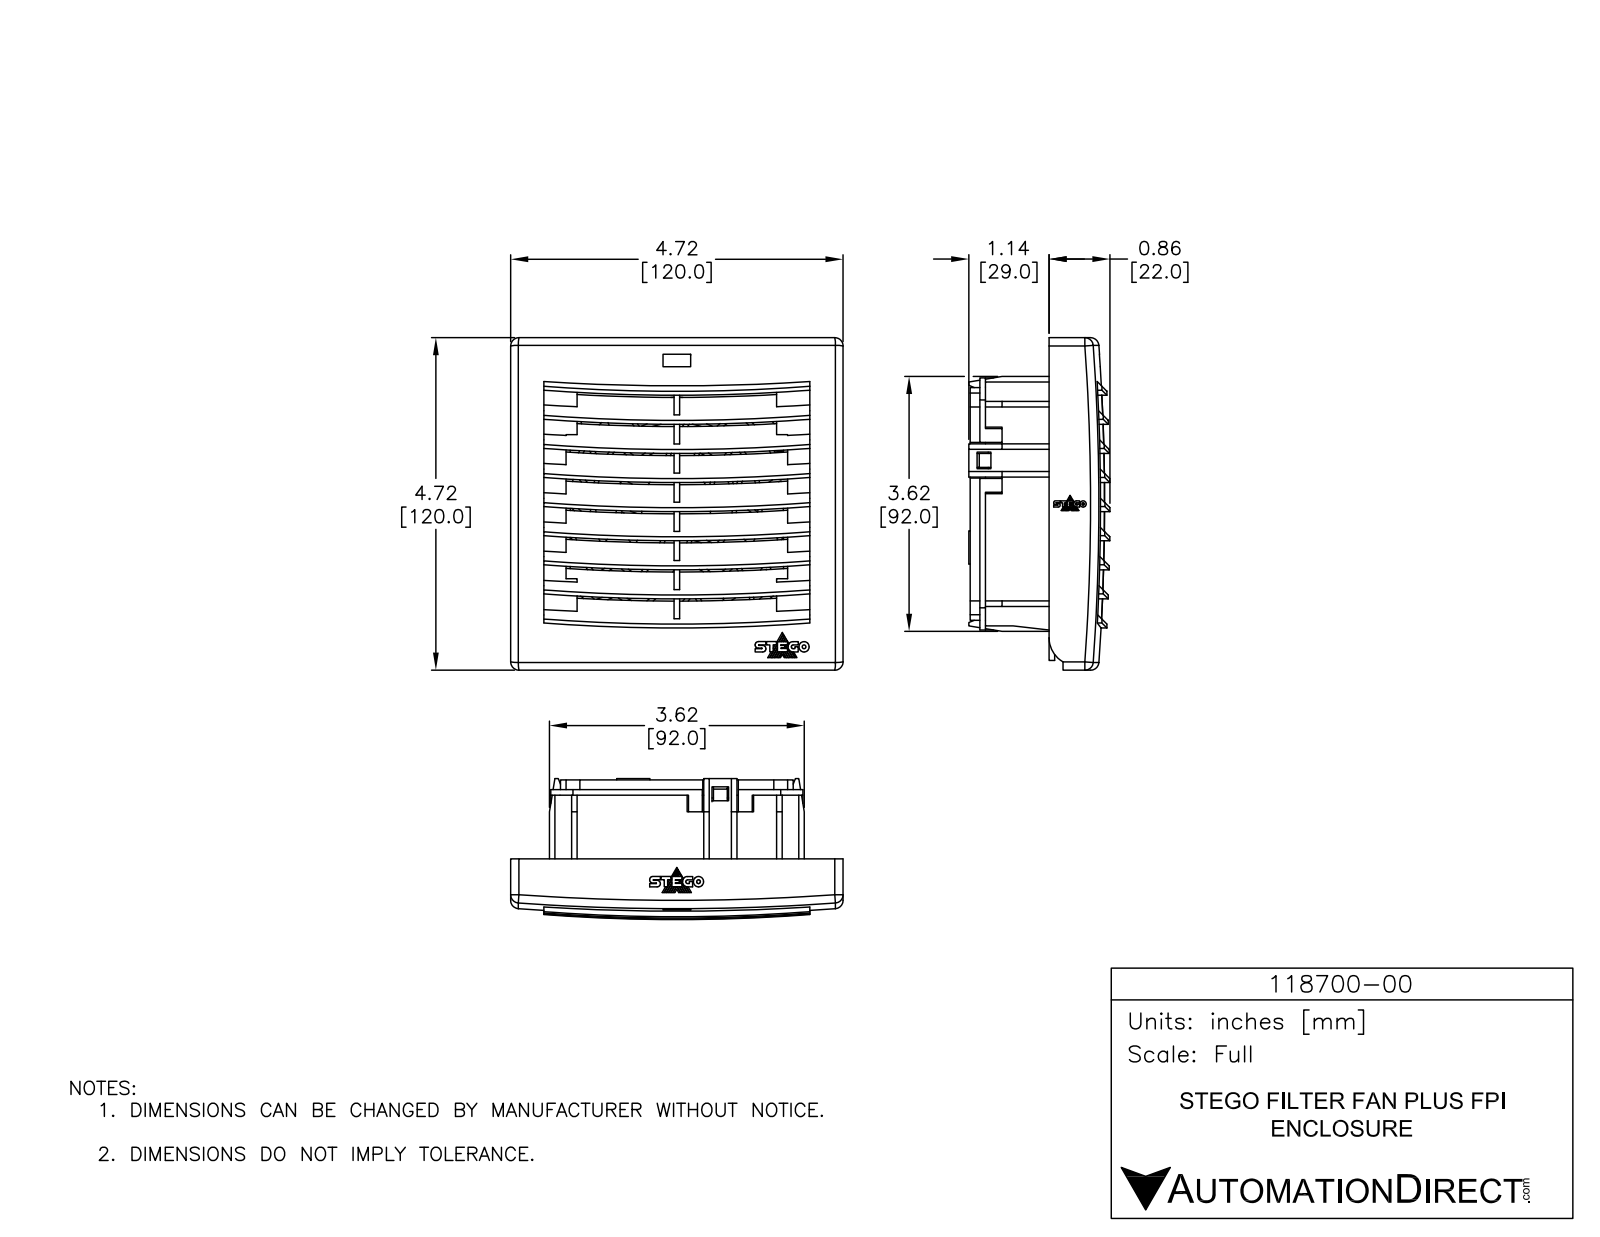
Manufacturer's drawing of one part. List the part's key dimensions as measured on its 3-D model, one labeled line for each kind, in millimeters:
Part name (STEP PRODUCT): 118700-00
STEP written by: SolidWorks 2018 (AUTOMOTIVE_DESIGN)
Units: millimetres
Bodies: 1 solid, 333 faces (187 planar, 146 cylindrical, 0 other)
Overall size (bounding box): 120 × 120 × 51
Volume: 189 100 mm³ · Surface area: 104 500 mm²
Round holes (diameter × count): ⌀50.7 ×1, ⌀63.4 ×1, ⌀78.2 ×1
Round bosses / shafts (diameter × count): ⌀67.6 ×1, ⌀54.9 ×1
Partial cylindrical surfaces — rounded edges, fillets, slot ends (radius × count): R219.2 ×15, R3 ×4, R13.7 ×1, R19 ×1, R21.1 ×1, R208.9 ×1
Main face-to-face distances: 1.5, 8, 3, 2.3, 89.7, 16.1, 6.1, 9.5, 14, 16.3
